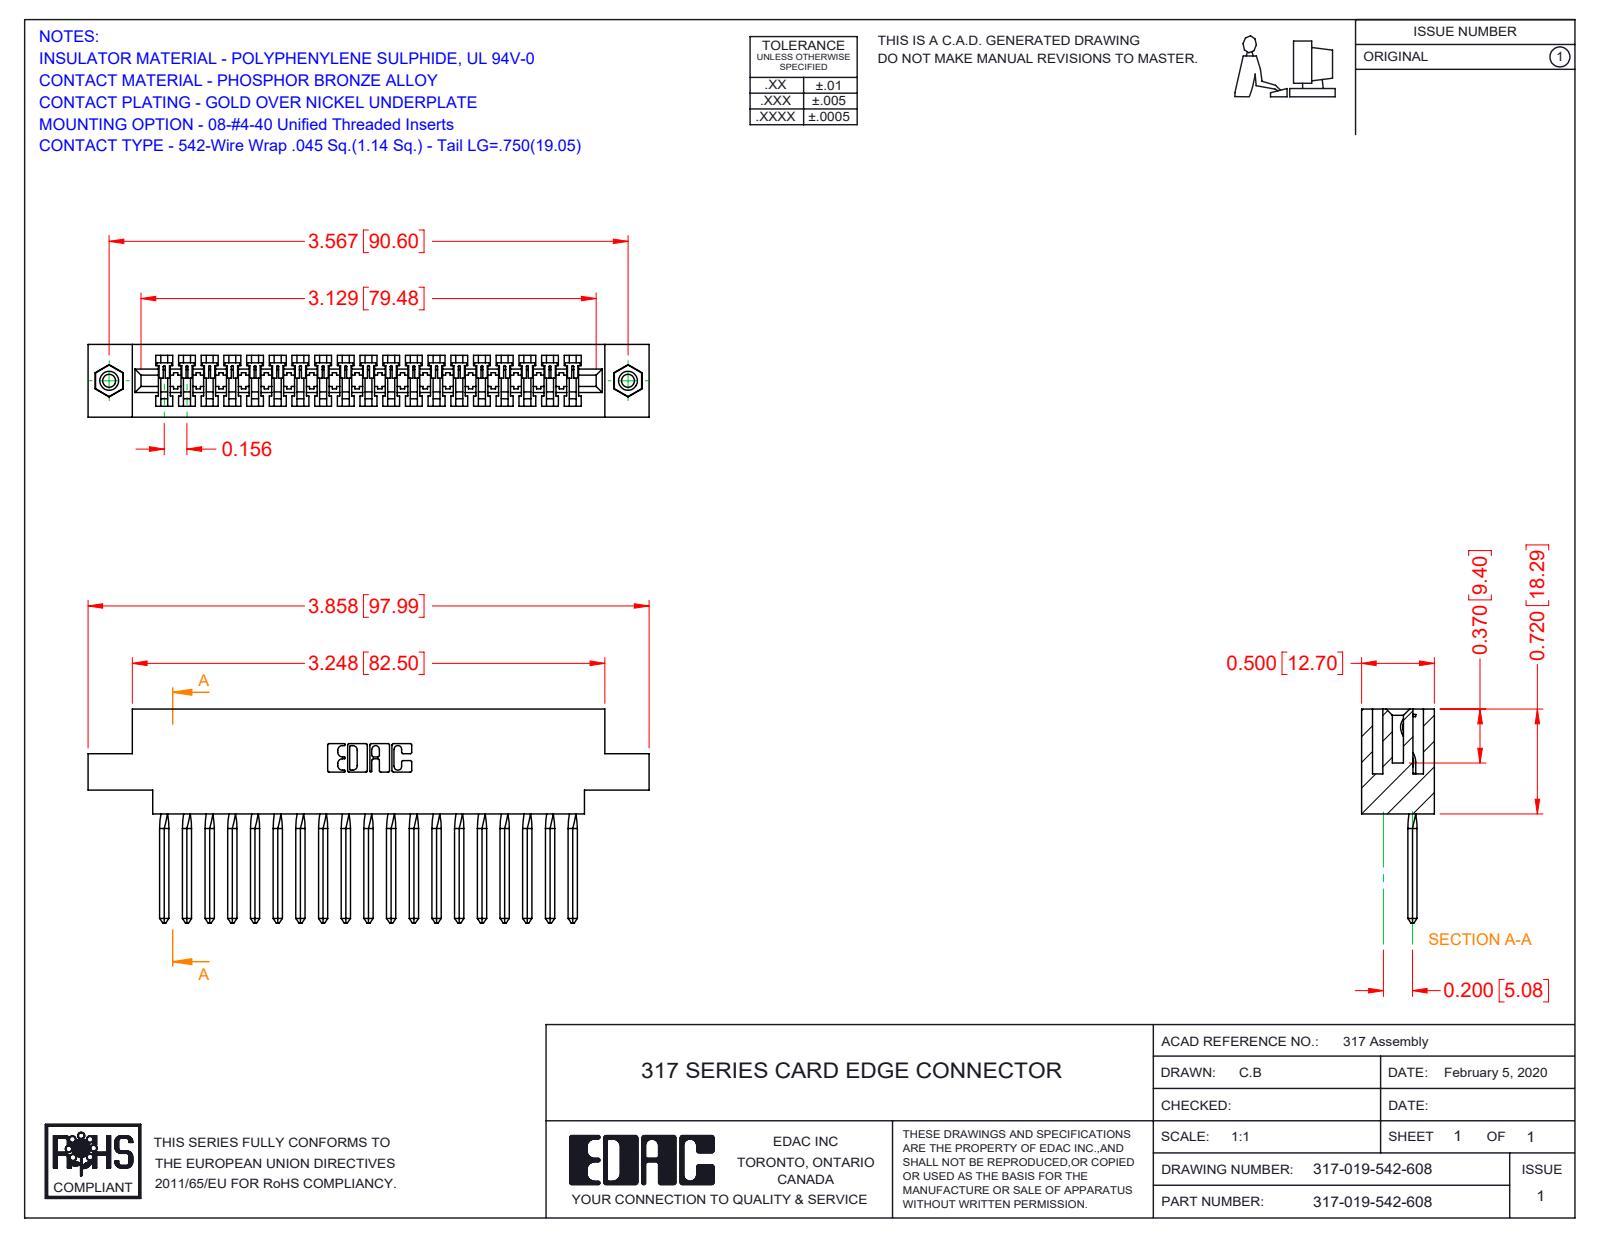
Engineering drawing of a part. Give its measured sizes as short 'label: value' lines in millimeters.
name: 317-019-542-678; 345-250-001_345-250-003-102; 317-290-003_542; 317 Part_.156 Dia - TI
written by: SolidWorks 2016 (CONFIG_CONTROL_DESIGN)
unit: mm
bodies: 22 solids, 1587 faces (1306 planar, 189 cylindrical, 92 other)
size: 98 × 37.3 × 12.7
volume: 14 500 mm³; area: 17 220 mm²
holes: 2× ⌀2.3, 2× ⌀3.2, 2× ⌀4
bosses: 2× ⌀3.9
rounds: 38× R0.2, 22× R0.3, 6× R0.2, 6× R0.8, 3× R0.7, 1× R1.9, 1× R2.3, 1× R2.5
face distances: 12.7, 1.9, 10.8, 8.9, 2.8, 3.5, 18.3, 7.1, 5.4, 7.3
hole spacings: 90.6
